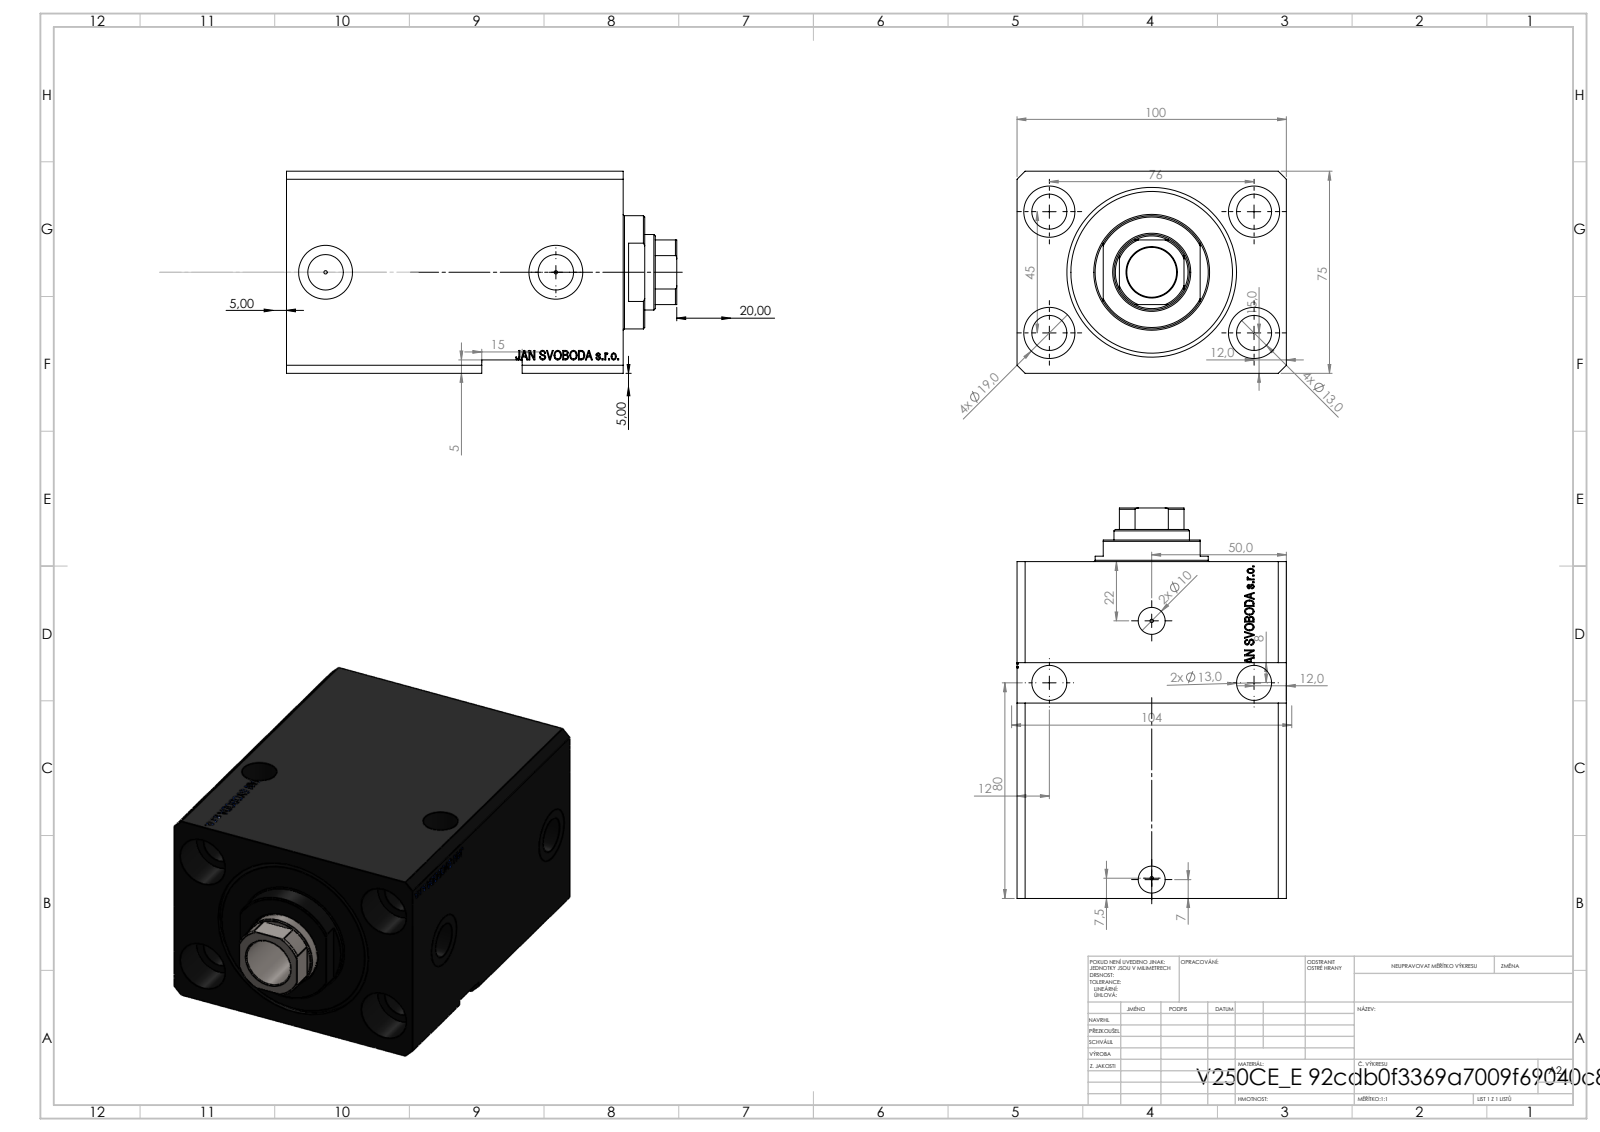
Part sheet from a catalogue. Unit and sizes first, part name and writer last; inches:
Units: inches
Overall size (bounding box): 5.709 × 3.937 × 2.953
Round holes (diameter × count): ⌀0.512 ×8, ⌀0.049 ×4, ⌀0.748 ×4, ⌀0.394 ×2, ⌀0.518 ×2, ⌀0.787 ×2, ⌀0.728 ×1, ⌀1.102 ×1, ⌀1.969 ×1, ⌀2.48 ×1
Round bosses / shafts (diameter × count): ⌀1.654 ×1
Partial cylindrical surfaces — rounded edges, fillets, slot ends (radius × count): R0.531 ×1
Main face-to-face distances: 2.953, 3.937, 4.921, 0.469, 4.453, 0.787, 4.134, 3.665, 2.756, 0.512
Hole centre spacings: 1.739, 2.992, 1.575, 1.749, 1.772, 1.968, 1.981, 2.896
Volume: 45.83 in³ · Surface area: 216.6 in²
Bodies: 3 solids, 954 faces (463 planar, 116 cylindrical, 375 other)
Part name (STEP PRODUCT): V250CE_C_VCP; V250CE_VC_E; V250CE_E_Body
STEP written by: SolidWorks 2019 (CONFIG_CONTROL_DESIGN)
